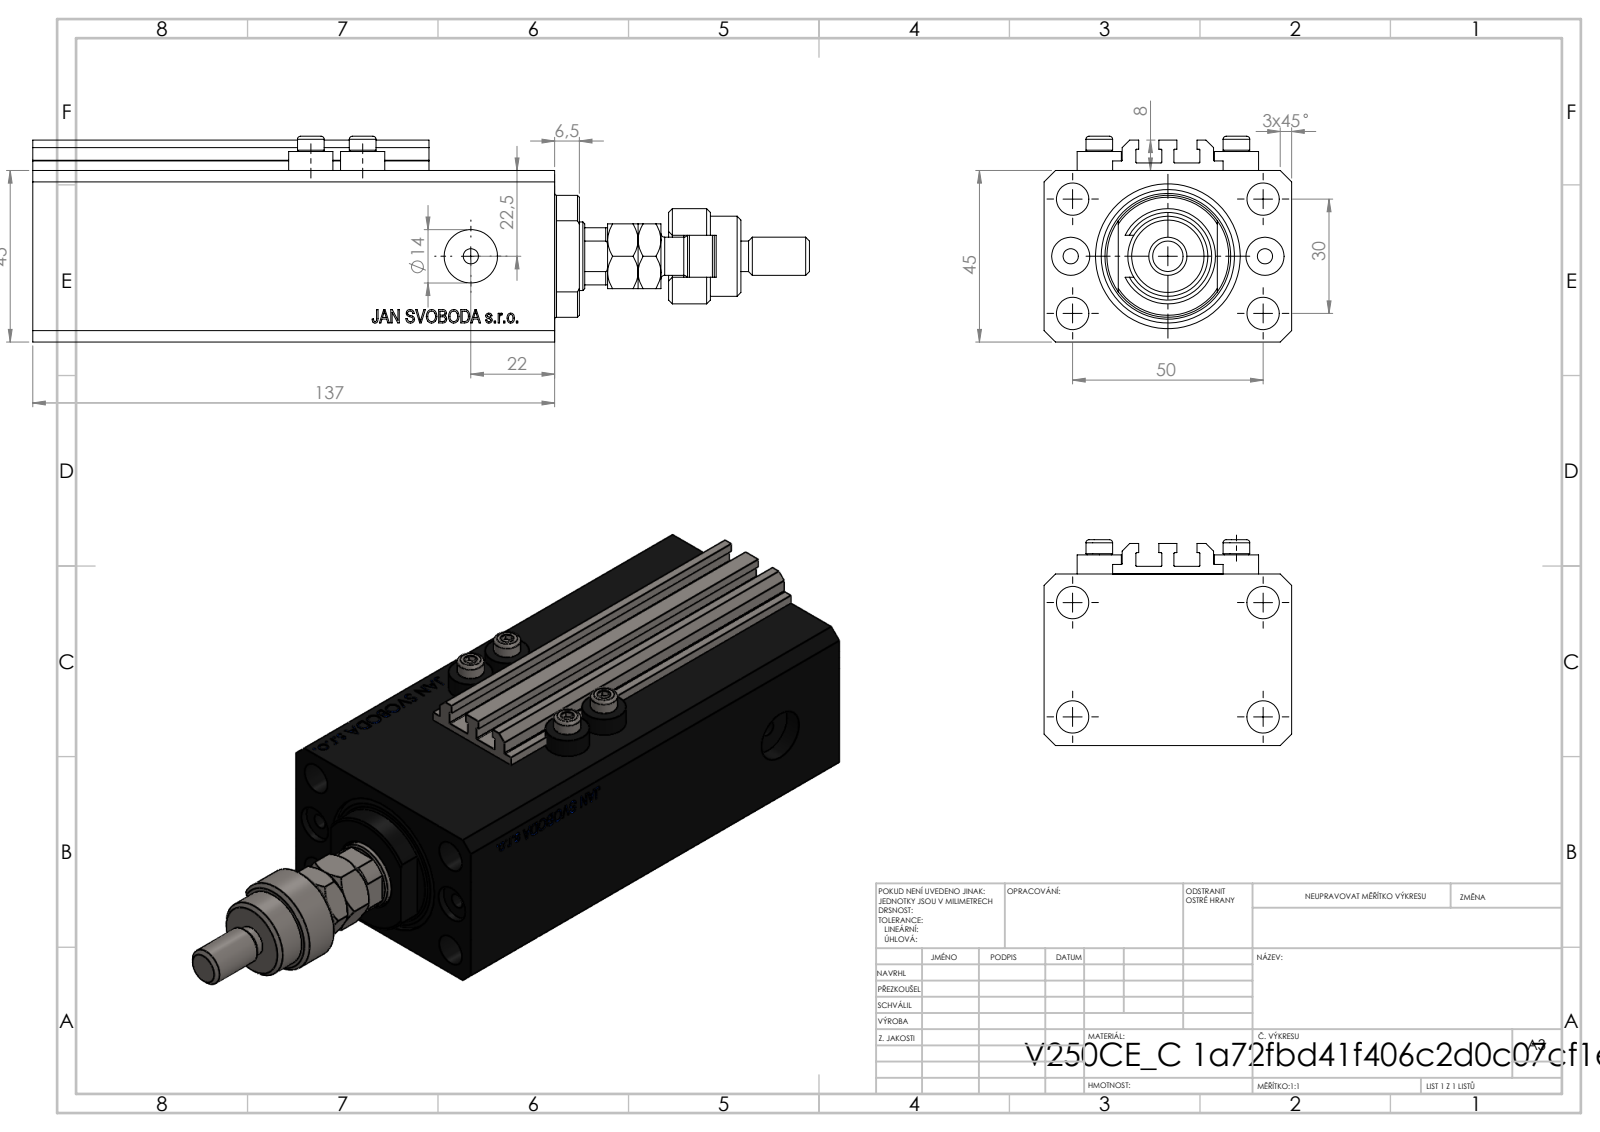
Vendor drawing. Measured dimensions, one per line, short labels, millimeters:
name: V250CE_C_Body; FEMALE_PART_FOR_DFA; MFA; ALLEN BOLT V250CE (+2 more)
written by: SolidWorks 2019 (CONFIG_CONTROL_DESIGN)
unit: mm
bodies: 10 solids, 1118 faces (531 planar, 99 cylindrical, 488 other)
size: 203.9 × 65 × 54
volume: 377 871 mm³; area: 98 209 mm²
holes: 8× ⌀4, 5× ⌀8.5, 2× ⌀10, 2× ⌀14, 1× ⌀18, 1× ⌀38
bosses: 4× ⌀11.6, 4× ⌀7, 1× ⌀25, 1× ⌀21, 1× ⌀16, 1× ⌀10, 1× ⌀8
rounds: 10× R0.2, 1× R5.5, 1× R8.5, 1× R8.75, 1× R16
face distances: 45, 65, 47, 2, 111.9, 137, 25.1, 2.5, 10, 53
hole spacings: 15.01, 29.15, 52.68, 13.6, 25.5, 30, 36, 38.48
